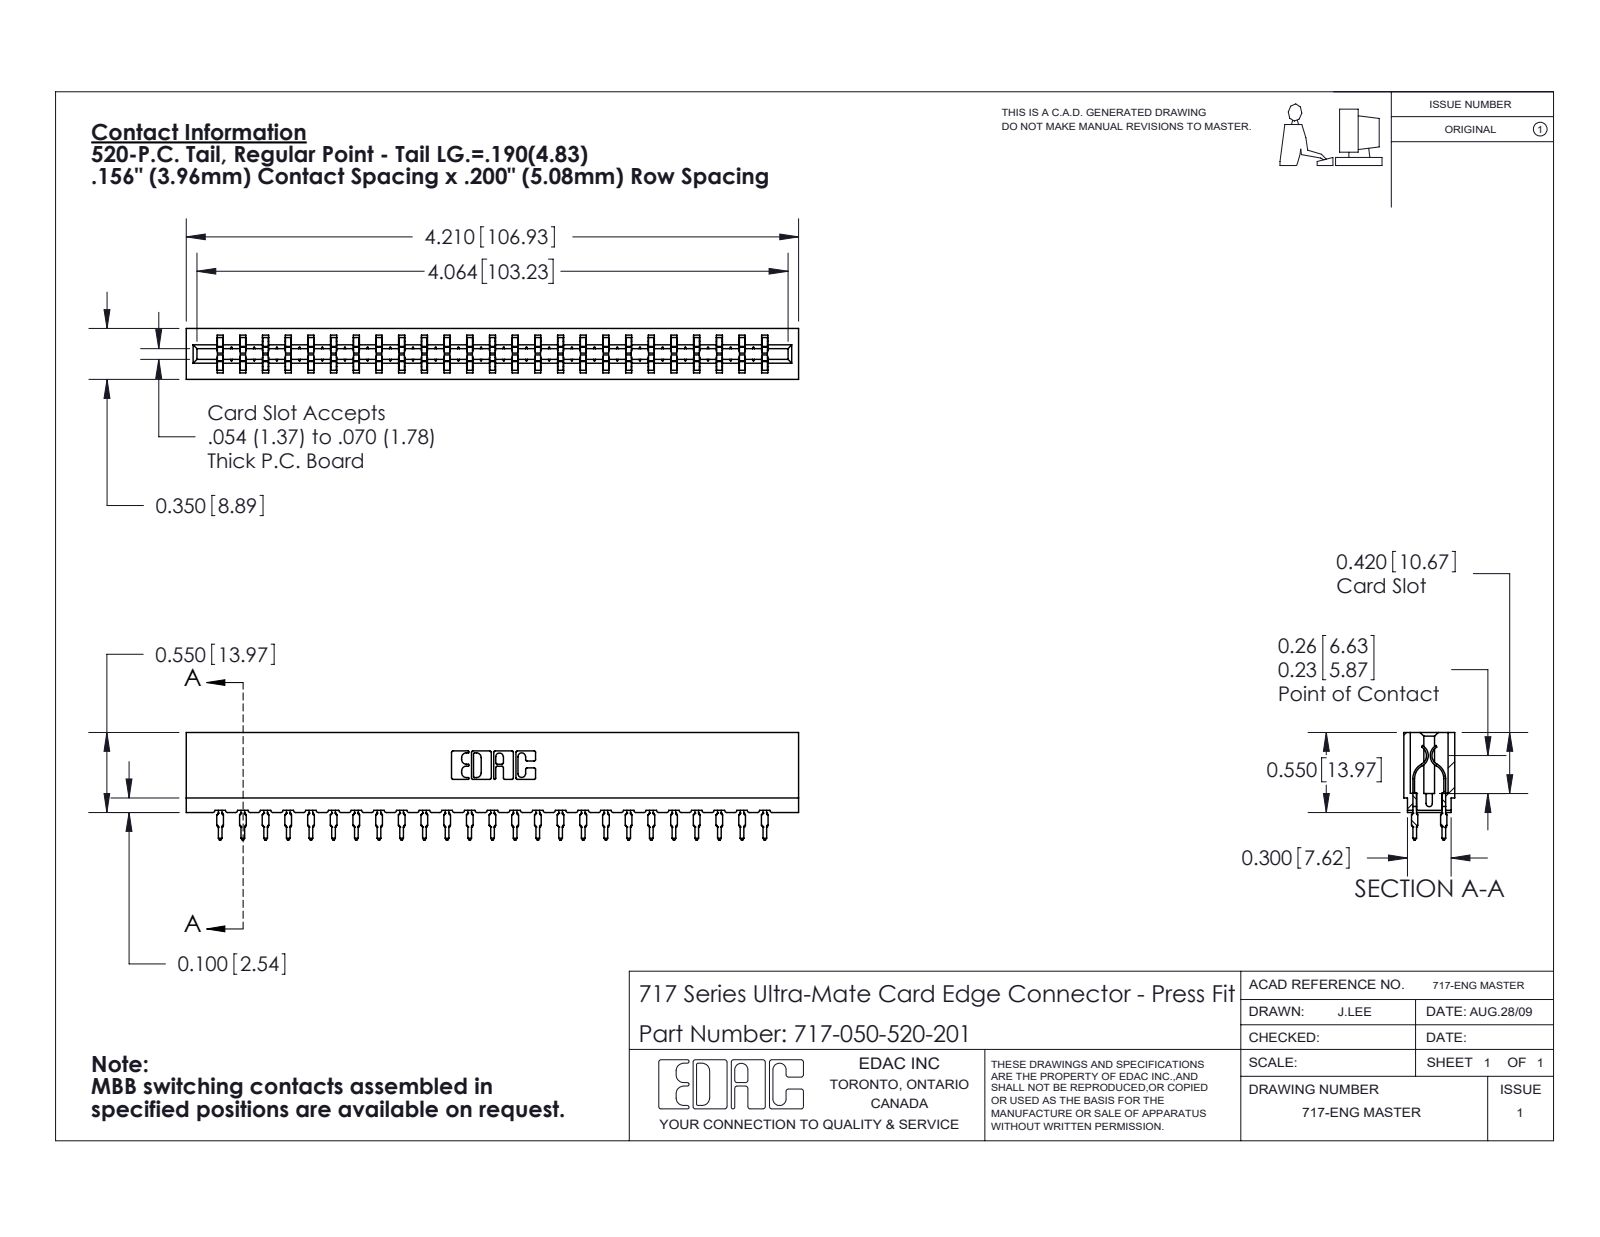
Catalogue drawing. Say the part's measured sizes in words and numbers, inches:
The part is named "717-050-520-201; 717 Part_Insulator Option - 06; 745-292-001_520". Its 3-D file was written by "SolidWorks 2020 (CONFIG_CONTROL_DESIGN)". It is 51 solids with 4594 faces: 2379 planar, 915 cylindrical and 1300 other. Overall it measures 4.21 by 0.739 by 0.35 inches. Its volume is 0.567 cubic inches and its surface area 21.29 square inches. Partial cylindrical surfaces (rounded edges, fillets, slot ends): 100 of radius 0.021, 50 of radius 0.015, 22 of radius 0.01, 8 of radius 0.005, 8 of radius 0.011, 6 of radius 0.007, 6 of radius 0.031, 3 of radius 0.026. The main face-to-face distances are 0.212, 0.138, 0.35, 0.156, 0.063, 0.287, 0.076, 0.149, 0.074, 0.624.
